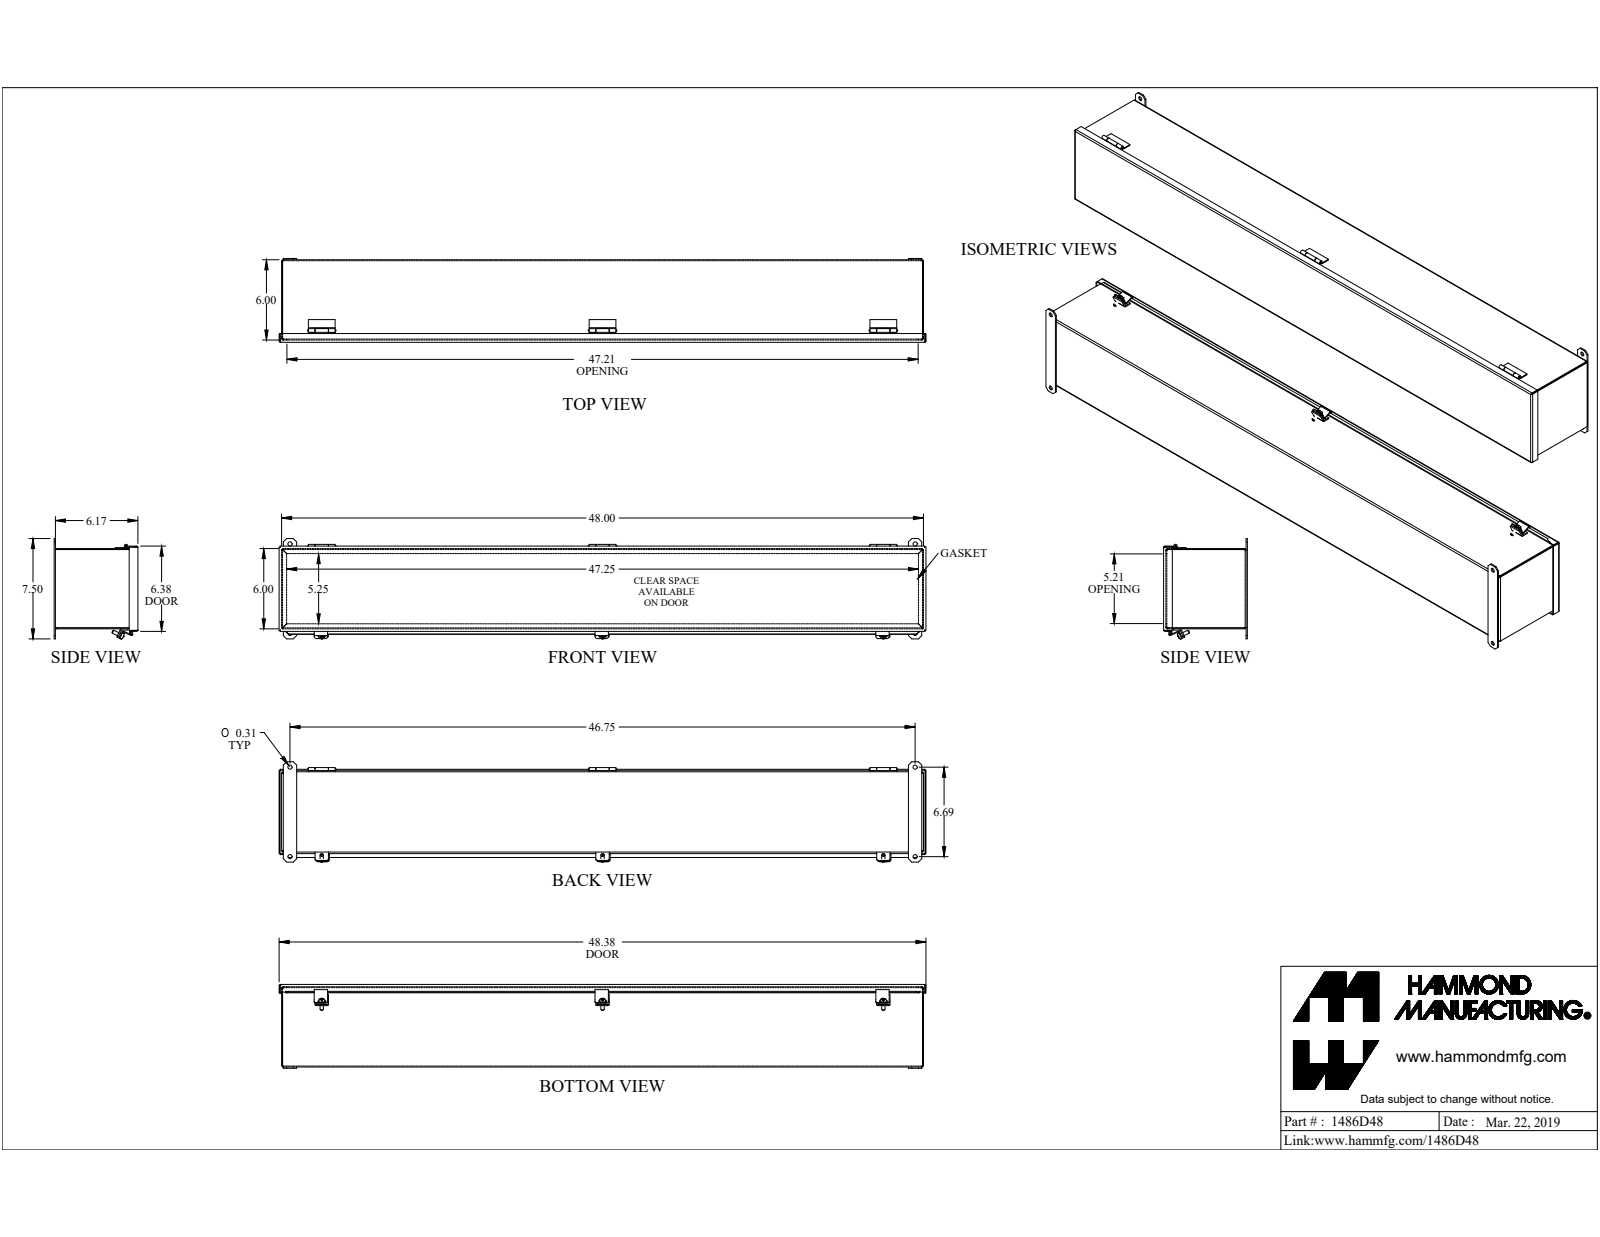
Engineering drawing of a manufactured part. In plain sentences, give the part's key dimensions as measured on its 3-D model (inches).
The part is named "1486D48". Its 3-D file was written by "SolidWorks 2019 (CONFIG_CONTROL_DESIGN)". It is 26 solids with 536 faces: 355 planar, 124 cylindrical and 57 other. Overall it measures 48.375 by 7.506 by 6.267 inches. Its volume is 113.5 cubic inches and its surface area 2 955 square inches. Round holes: 4 of diameter 0.313, 3 of diameter 0.213, 1 of diameter 0.125. Round bosses or shafts: 3 of diameter 0.48, 3 of diameter 0.246, 1 of diameter 0.275, 1 of diameter 0.125. Partial cylindrical surfaces (rounded edges, fillets, slot ends): 13 of radius 0.036, 13 of radius 0.108, 12 of radius 0.188, 12 of radius 0.25, 6 of radius 0.01, 6 of radius 0.141, 2 of radius 0.029, 2 of radius 0.086. The main face-to-face distances are 0.072, 5.928, 6.1, 6, 5.856, 6.172, 6.028, 0.187, 0.259, 5.913. The hole center spacings are 6.688, 21, 46.75, 47.226, 42.
